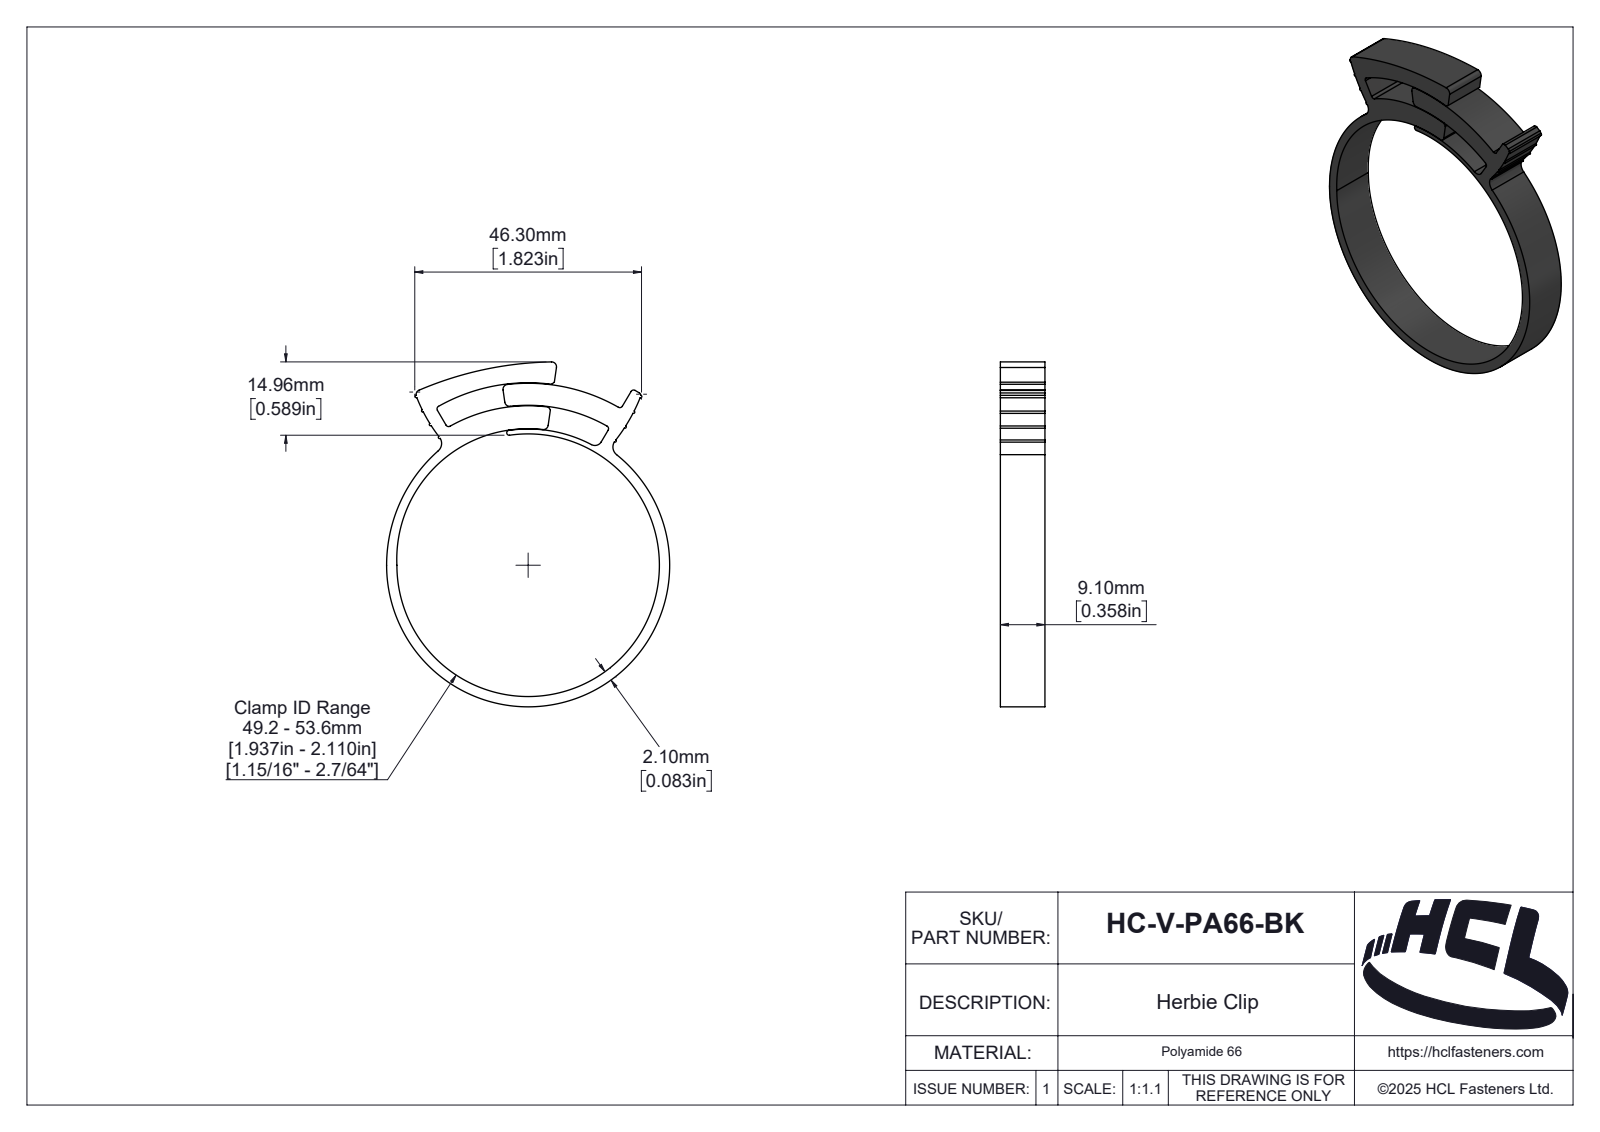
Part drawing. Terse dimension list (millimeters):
name: HC-V-PA66-BK
written by: SolidWorks 2025 (AUTOMOTIVE_DESIGN)
unit: mm
bodies: 1 solid, 162 faces (13 planar, 100 cylindrical, 49 other)
size: 70.39 × 57.8 × 9.1
volume: 6 294 mm³; area: 6 122 mm²
rounds: 8× R0.25, 6× R0.6, 5× R1, 2× R2, 1× R0.17, 1× R0.5, 1× R0.67, 1× R0.84
face distances: 9.1
